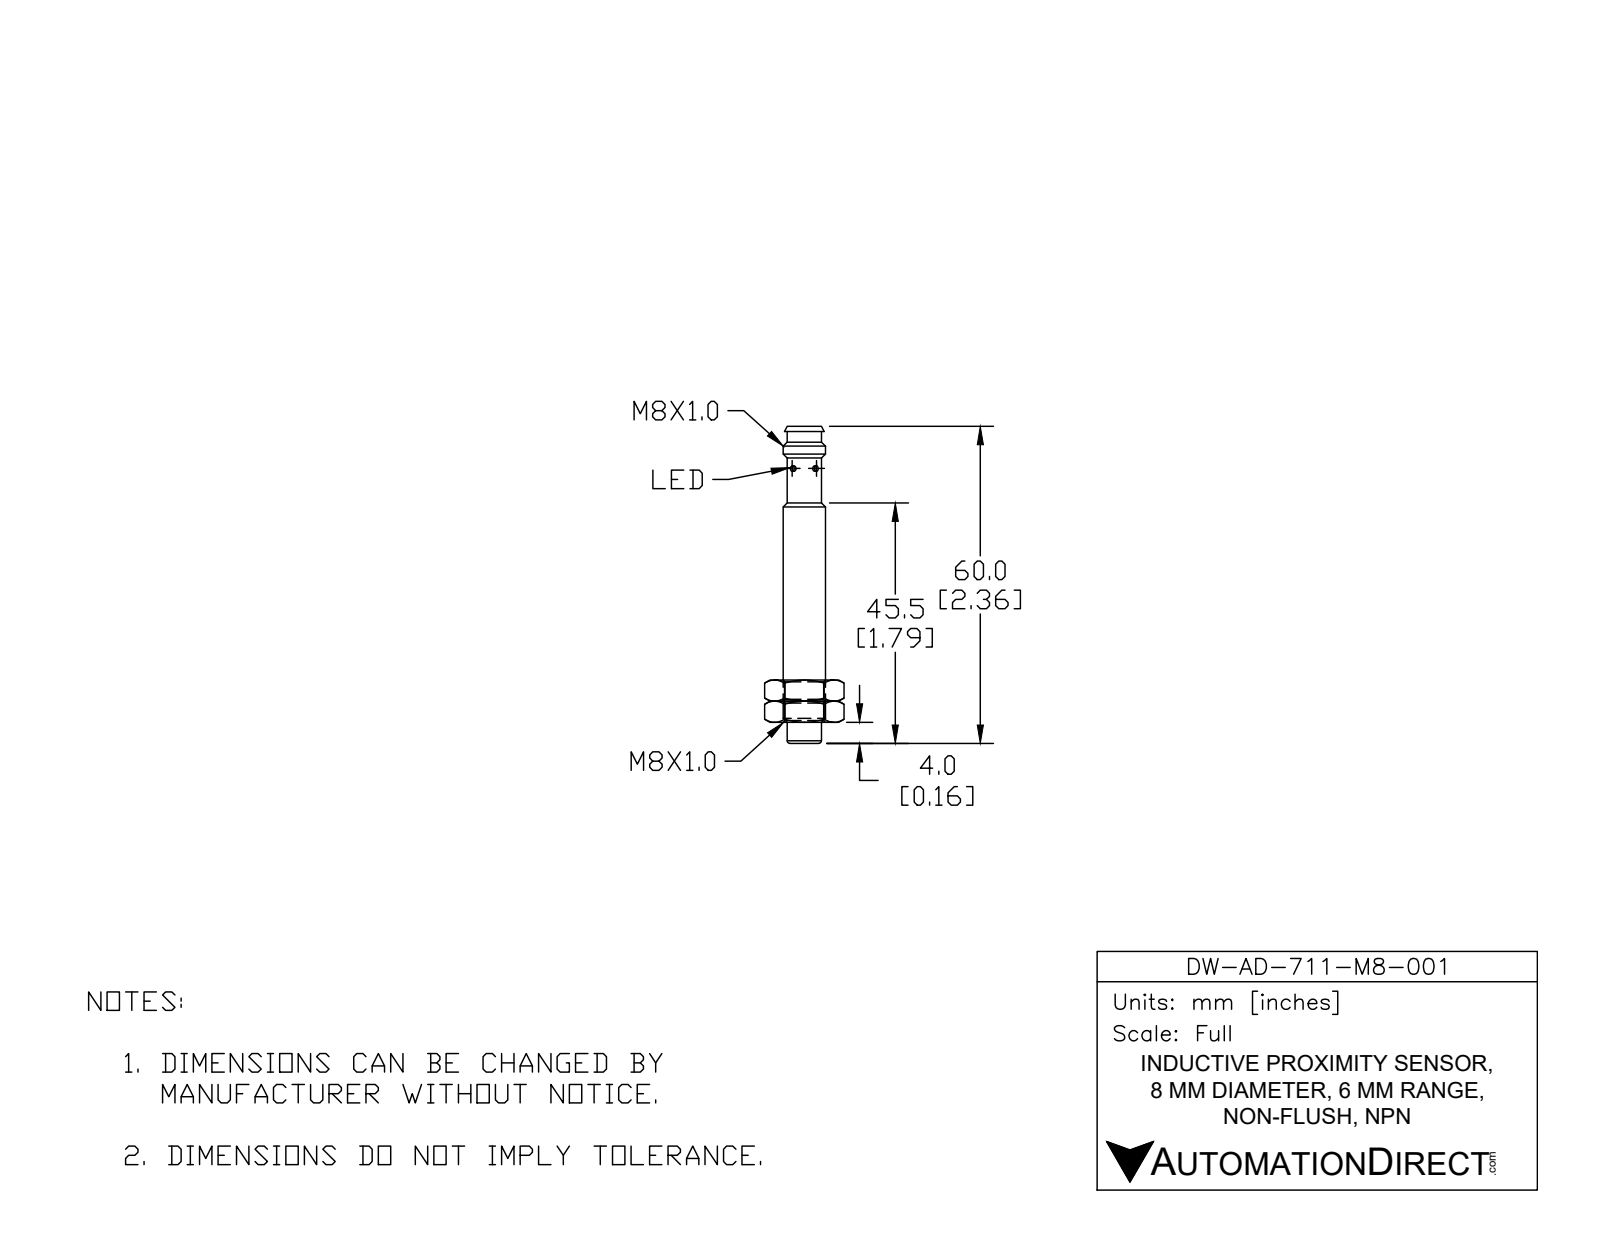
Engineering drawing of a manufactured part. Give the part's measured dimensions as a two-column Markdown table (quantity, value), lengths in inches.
| quantity | value |
| --- | --- |
| part name | DW-AS-711-M8-001 |
| STEP written by | SolidWorks 2017 (AUTOMOTIVE_DESIGN) |
| units | inches |
| bodies | 1 solid, 49 faces (15 planar, 22 cylindrical, 12 other) |
| overall size | 2.362 × 0.315 × 0.315 |
| volume | 0.16 in³ |
| surface area | 2.613 in² |
| round holes (diameter × count) | 0.071 × 2 |
| round bosses / shafts (diameter × count) | 0.039 × 3, 0.315 × 1, 0.272 × 1, 0.256 × 1, 0.236 × 1 |
| partial cylindrical surfaces (radius × count) | 0.118 × 1 |
| main face-to-face distances | 2.179, 0.157, 2.362, 0.183, 2.002, 0.177, 0.36 |
